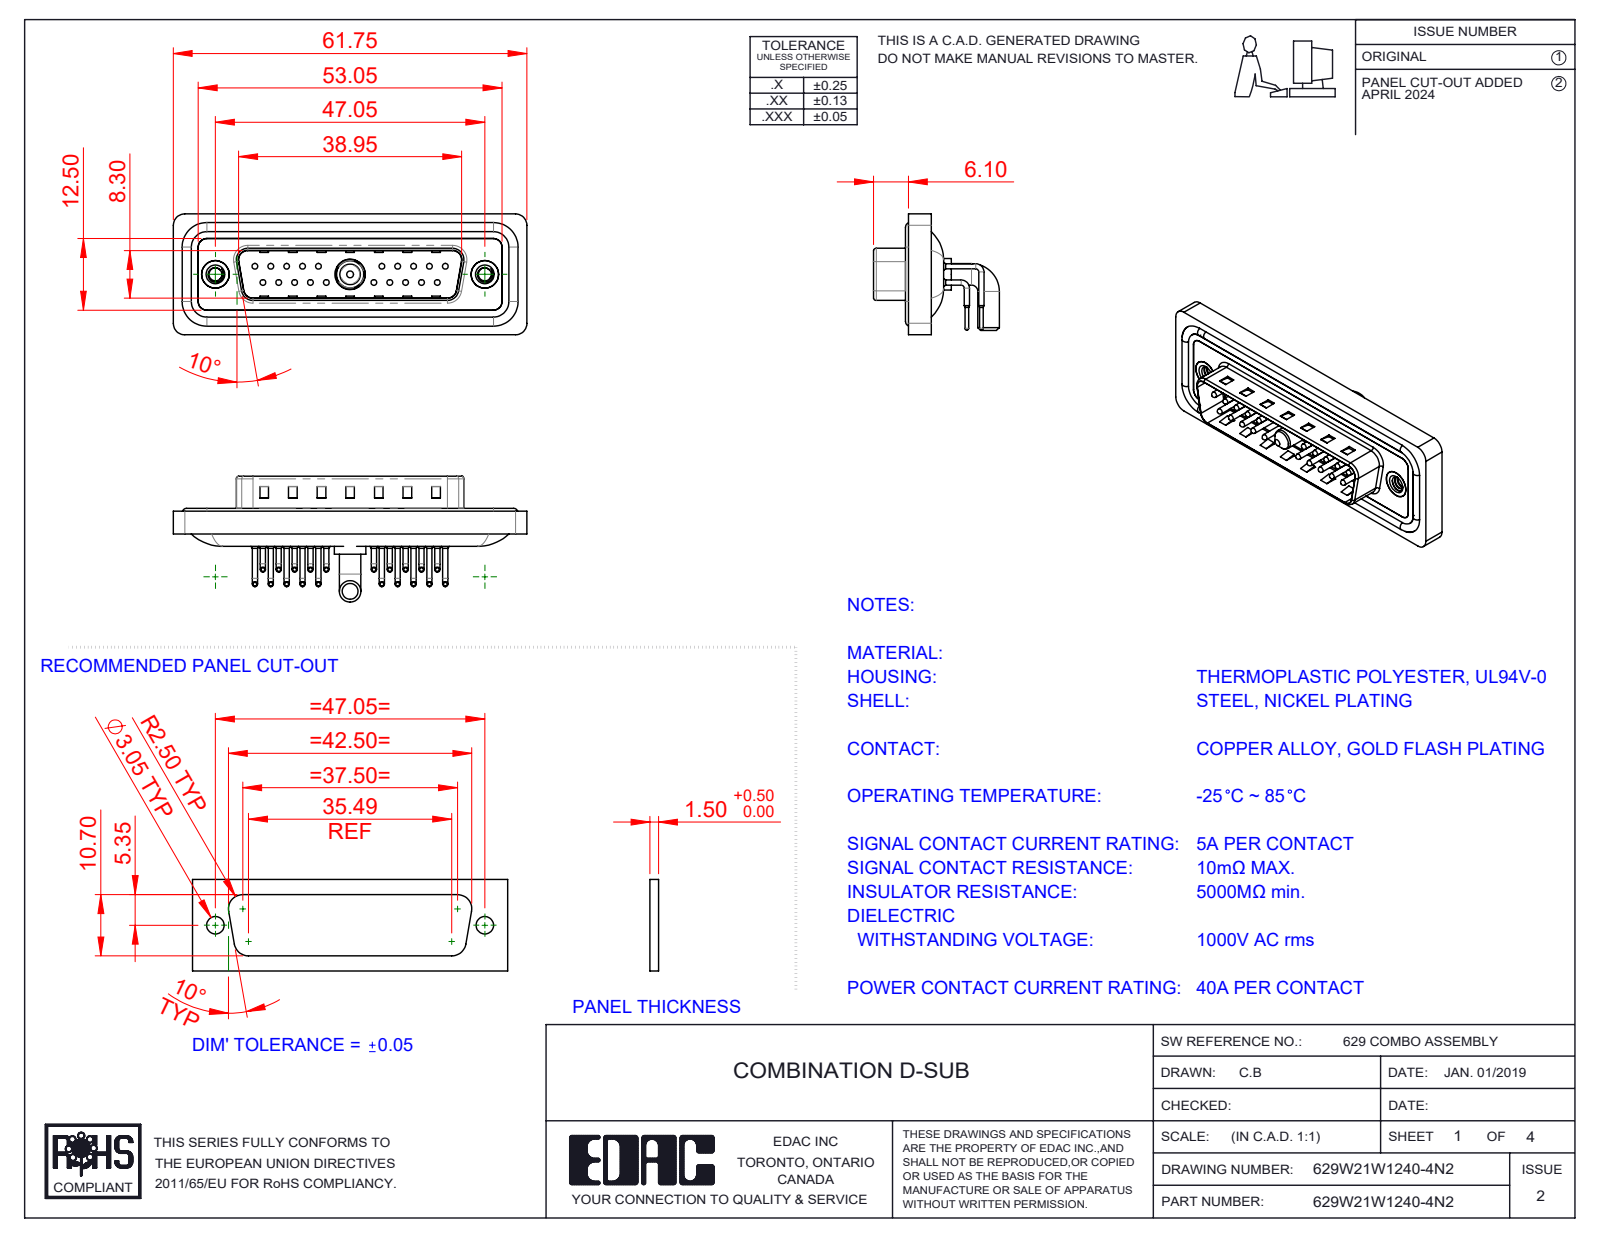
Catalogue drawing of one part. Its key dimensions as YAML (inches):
part_name: "629Combo Threaded Rivet_2; Power Pin_40A RA; 629Combo Contact Row 1; 629Combo Shell Front_25 Contacts (+5 more)"
step_written_by: "SolidWorks 2023 (CONFIG_CONTROL_DESIGN)"
units: inches
bodies: {solids: 29, faces: 2726, planar: 1499, cylindrical: 929, other: 298}
overall_size: [2.431, 0.865, 0.831]
volume: 0.458
surface_area: 19.79
round_holes:
  - {diameter: 0.03, count: 20}
  - {diameter: 0.063, count: 20}
  - {diameter: 0.079, count: 20}
  - {diameter: 0.089, count: 2}
  - {diameter: 0.157, count: 2}
  - {diameter: 0.189, count: 2}
  - {diameter: 0.197, count: 2}
  - {diameter: 0.191, count: 1}
  - {diameter: 0.209, count: 1}
round_bosses_or_shafts:
  - {diameter: 0.035, count: 40}
  - {diameter: 0.059, count: 20}
  - {diameter: 0.039, count: 20}
  - {diameter: 0.026, count: 20}
  - {diameter: 0.063, count: 4}
  - {diameter: 0.193, count: 2}
  - {diameter: 0.148, count: 2}
  - {diameter: 0.217, count: 1}
partial_cylinders:
  - {radius: 0.04, count: 20}
  - {radius: 0.059, count: 18}
  - {radius: 0.079, count: 18}
  - {radius: 0.02, count: 8}
  - {radius: 0.063, count: 8}
  - {radius: 0.01, count: 4}
  - {radius: 0.024, count: 4}
  - {radius: 0.026, count: 4}
face_to_face_distances: [0.016, 0.114, 0.031, 0.161, 0.043, 0.083, 0.063, 0.177, 0.059, 0.098]
hole_center_spacings: [0.124, 0.109, 0.218, 0.327, 0.198, 0.763, 0.826, 0.872]
